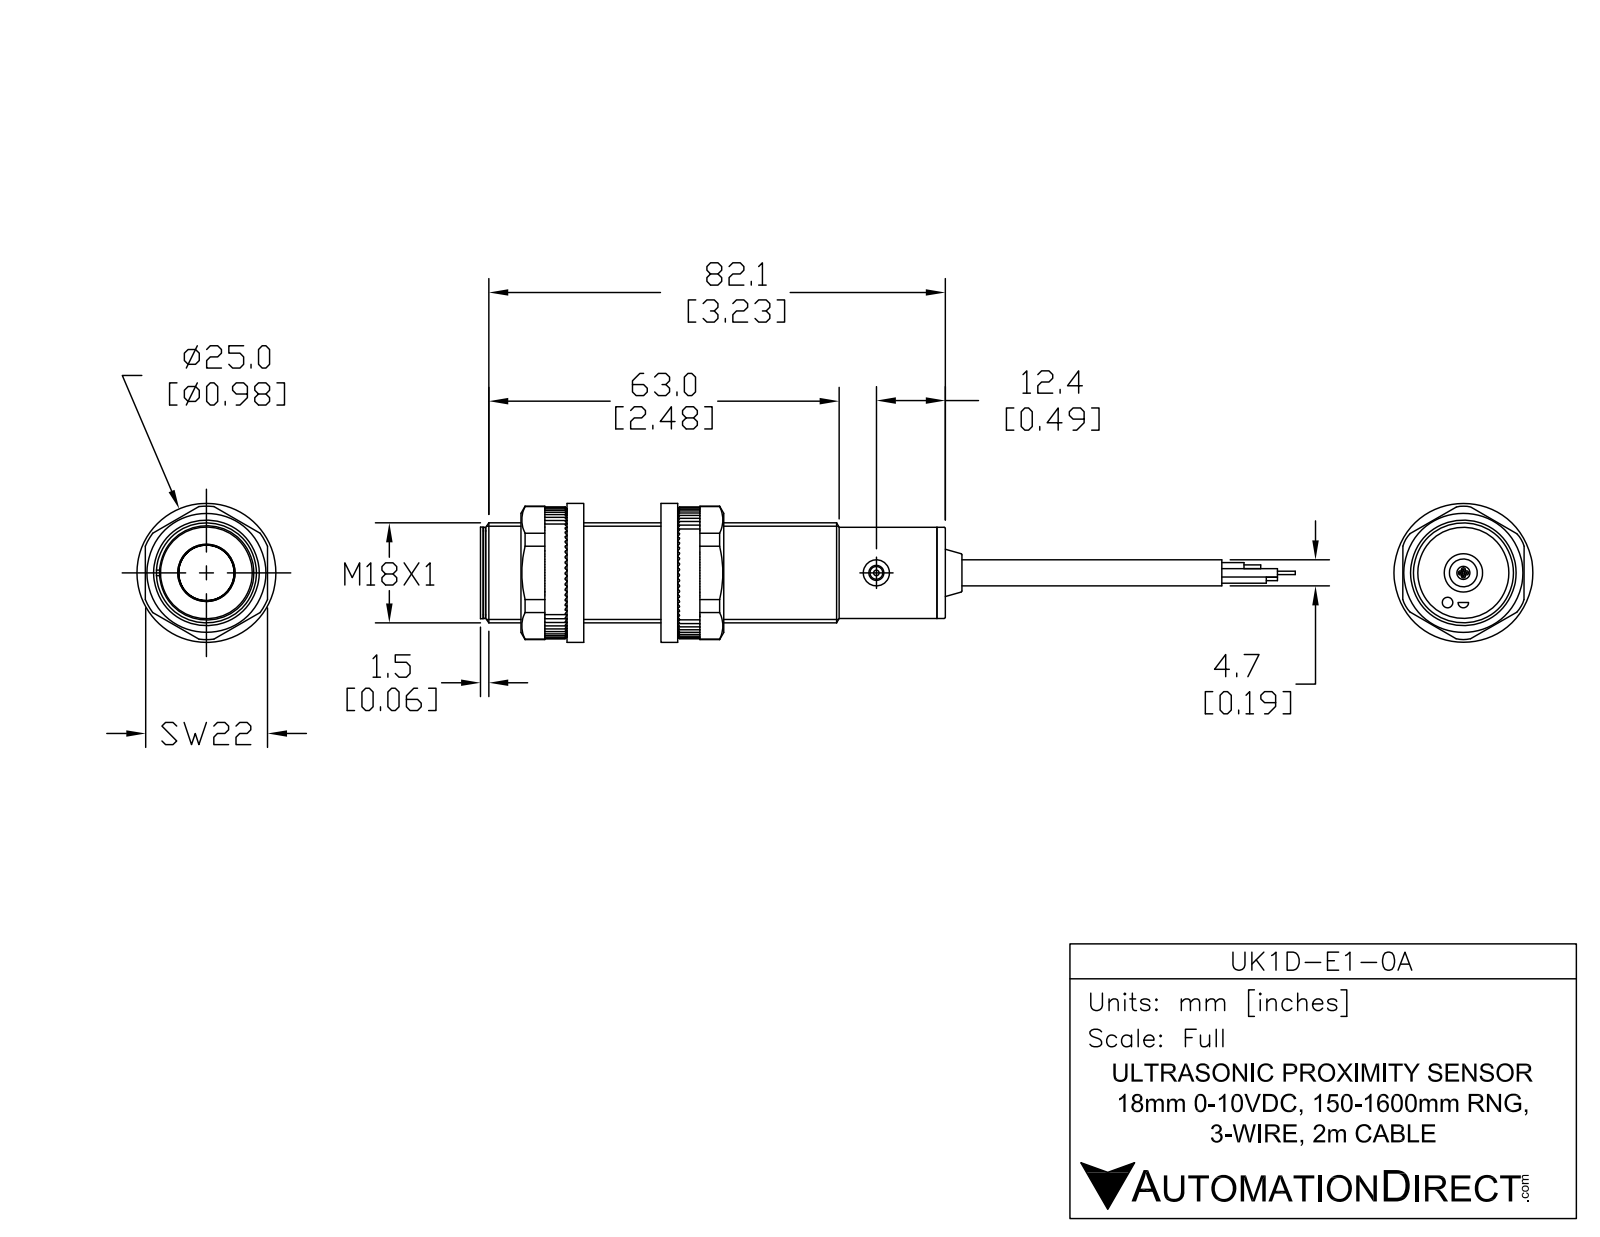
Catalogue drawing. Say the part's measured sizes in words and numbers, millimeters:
The part is named "UK1D-E1-0A". Its 3-D file was written by "SolidWorks 2017 (AUTOMOTIVE_DESIGN)". It is 6 solids with 55 faces: 17 planar, 24 cylindrical and 14 other. Overall it measures 122.7 by 18 by 18 millimeters. Its volume is 21 060 cubic millimeters and its surface area 6 897 square millimeters. Round holes: 2 of diameter 4.7, 1 of diameter 2.7. Round bosses or shafts: 1 of diameter 18, 1 of diameter 16.4, 1 of diameter 15.8, 1 of diameter 9.5, 1 of diameter 4.8, 1 of diameter 2.3. The main face-to-face distances are 81.1, 82.6, 1.5, 1, 82.1, 83.6, 1, 82.1, 83.6, 82.7.
